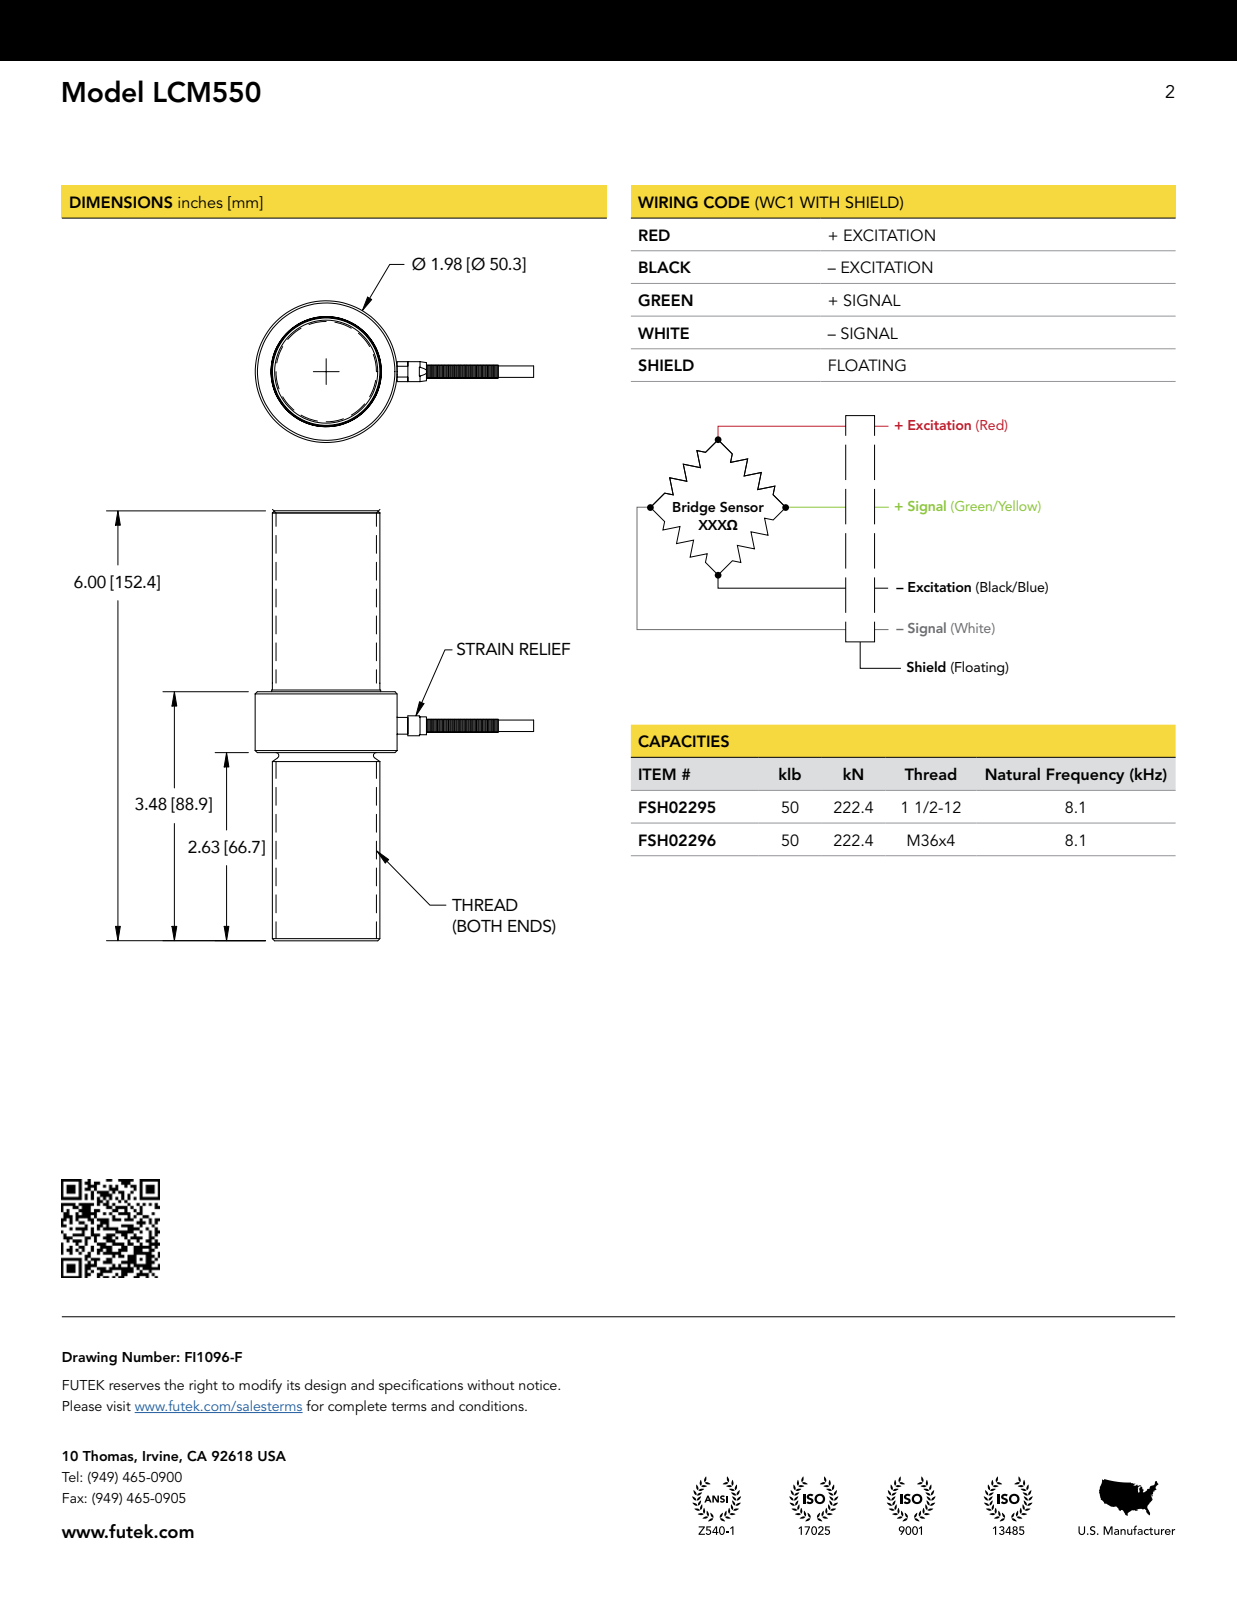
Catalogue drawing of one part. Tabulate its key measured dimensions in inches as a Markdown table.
| quantity | value |
| --- | --- |
| part name | LCM550 cable 1.5-12 thread; ~~$F1677-C |
| STEP written by | Autodesk Inventor 2008 (AUTOMOTIVE_DESIGN) |
| units | inches |
| bodies | 1 solid, 181 faces (58 planar, 40 cylindrical, 83 other) |
| overall size | 6 × 5.165 × 1.98 |
| volume | 11.7 in³ |
| surface area | 47.23 in² |
| round holes (diameter × count) | 0.16 × 1, 0.189 × 1, 0.21 × 1, 0.22 × 1, 0.228 × 1, 1.54 × 1, 1.61 × 1 |
| round bosses / shafts (diameter × count) | 0.13 × 3, 1.98 × 1, 1.538 × 1, 1.52 × 1, 1.5 × 1, 0.278 × 1, 0.225 × 1, 0.205 × 1 |
| partial cylindrical surfaces (radius × count) | 0.065 × 1, 0.085 × 1 |
| main face-to-face distances | 6, 3.305, 2.695, 2.455, 0.85, 3.545, 0.07, 3.375, 0.92, 2.625 |
